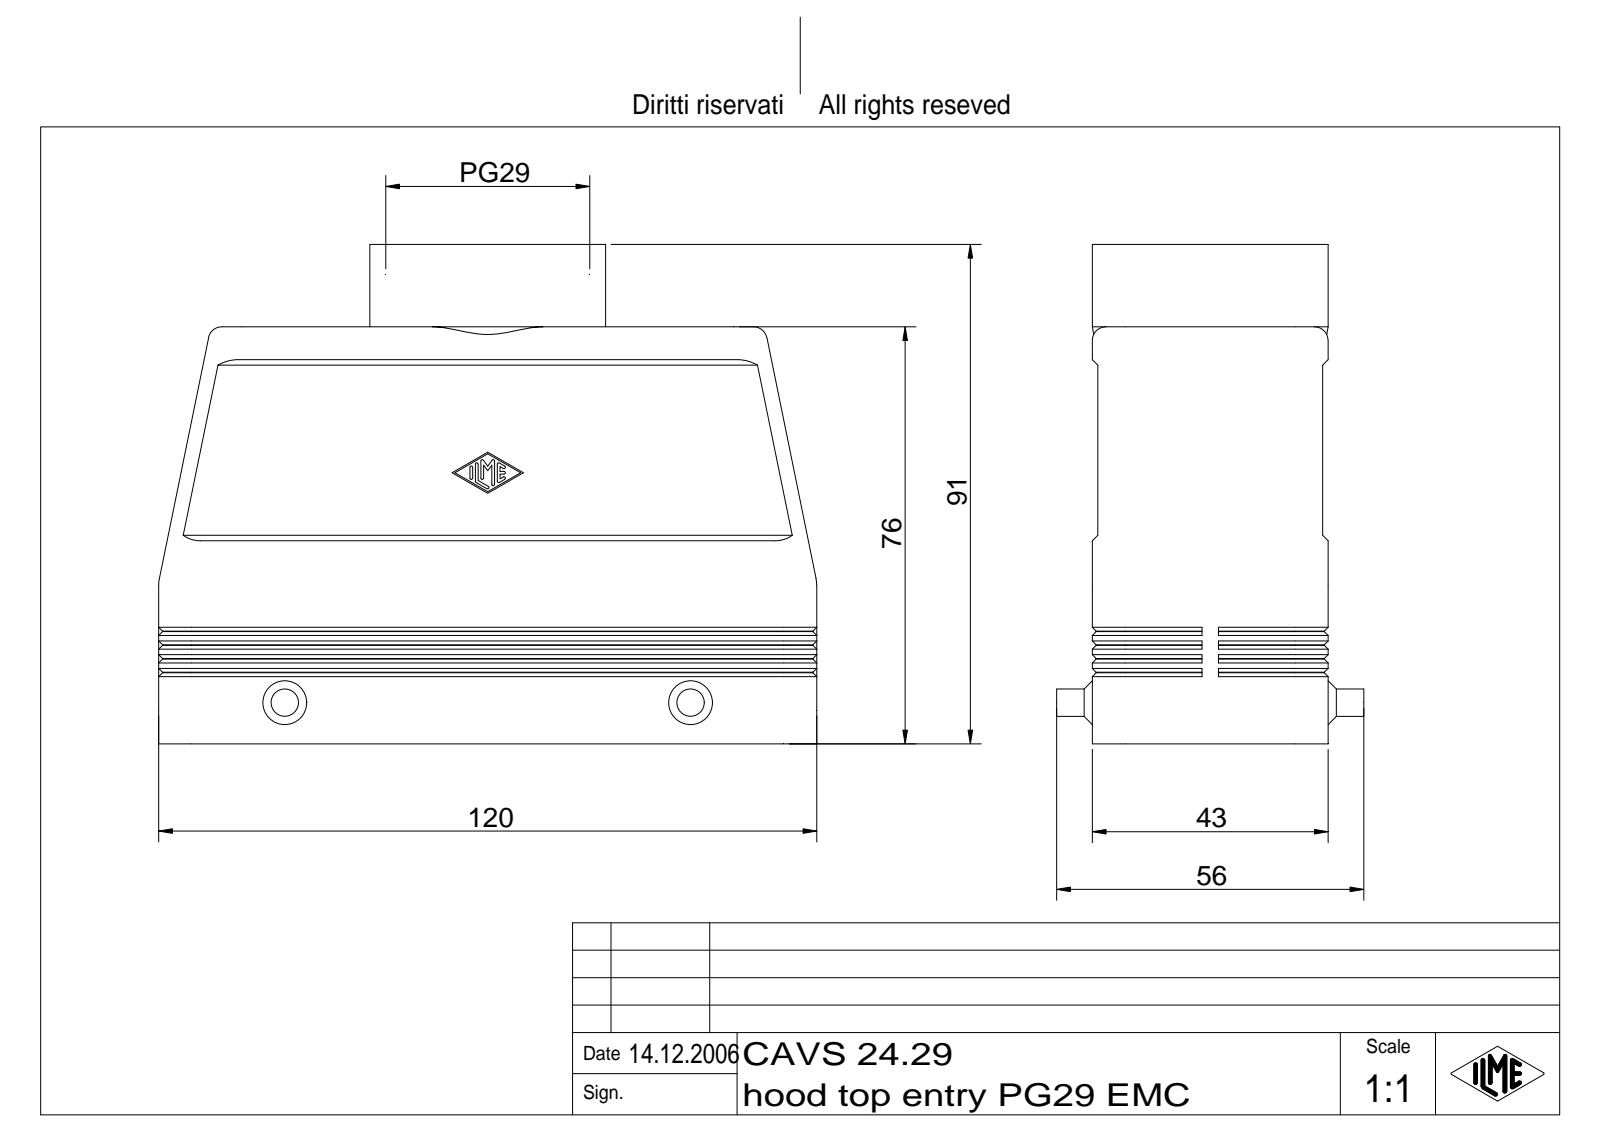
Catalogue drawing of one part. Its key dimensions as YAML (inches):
part_name: "CAO Tüllengehäuse 2 Bügel für einen Einsatz"
step_written_by: "Autodesk Inventor 7 (AUTOMOTIVE_DESIGN)"
units: inches
bodies: {solids: 1, faces: 413, planar: 153, cylindrical: 108, other: 152}
overall_size: [4.724, 3.583, 2.205]
volume: 5.457
surface_area: 88.2
round_holes:
  - {diameter: 1.318, count: 1}
  - {diameter: 1.397, count: 1}
round_bosses_or_shafts:
  - {diameter: 0.197, count: 2}
  - {diameter: 1.693, count: 1}
  - {diameter: 1.357, count: 1}
partial_cylinders:
  - {radius: 0.01, count: 14}
  - {radius: 0.236, count: 10}
  - {radius: 0.079, count: 4}
  - {radius: 0.098, count: 4}
  - {radius: 0.118, count: 4}
  - {radius: 0.209, count: 2}
face_to_face_distances: [0.118, 1.457, 1.575, 0.039, 0.079, 1.654, 1.535, 1.693, 1.614, 0.472]
